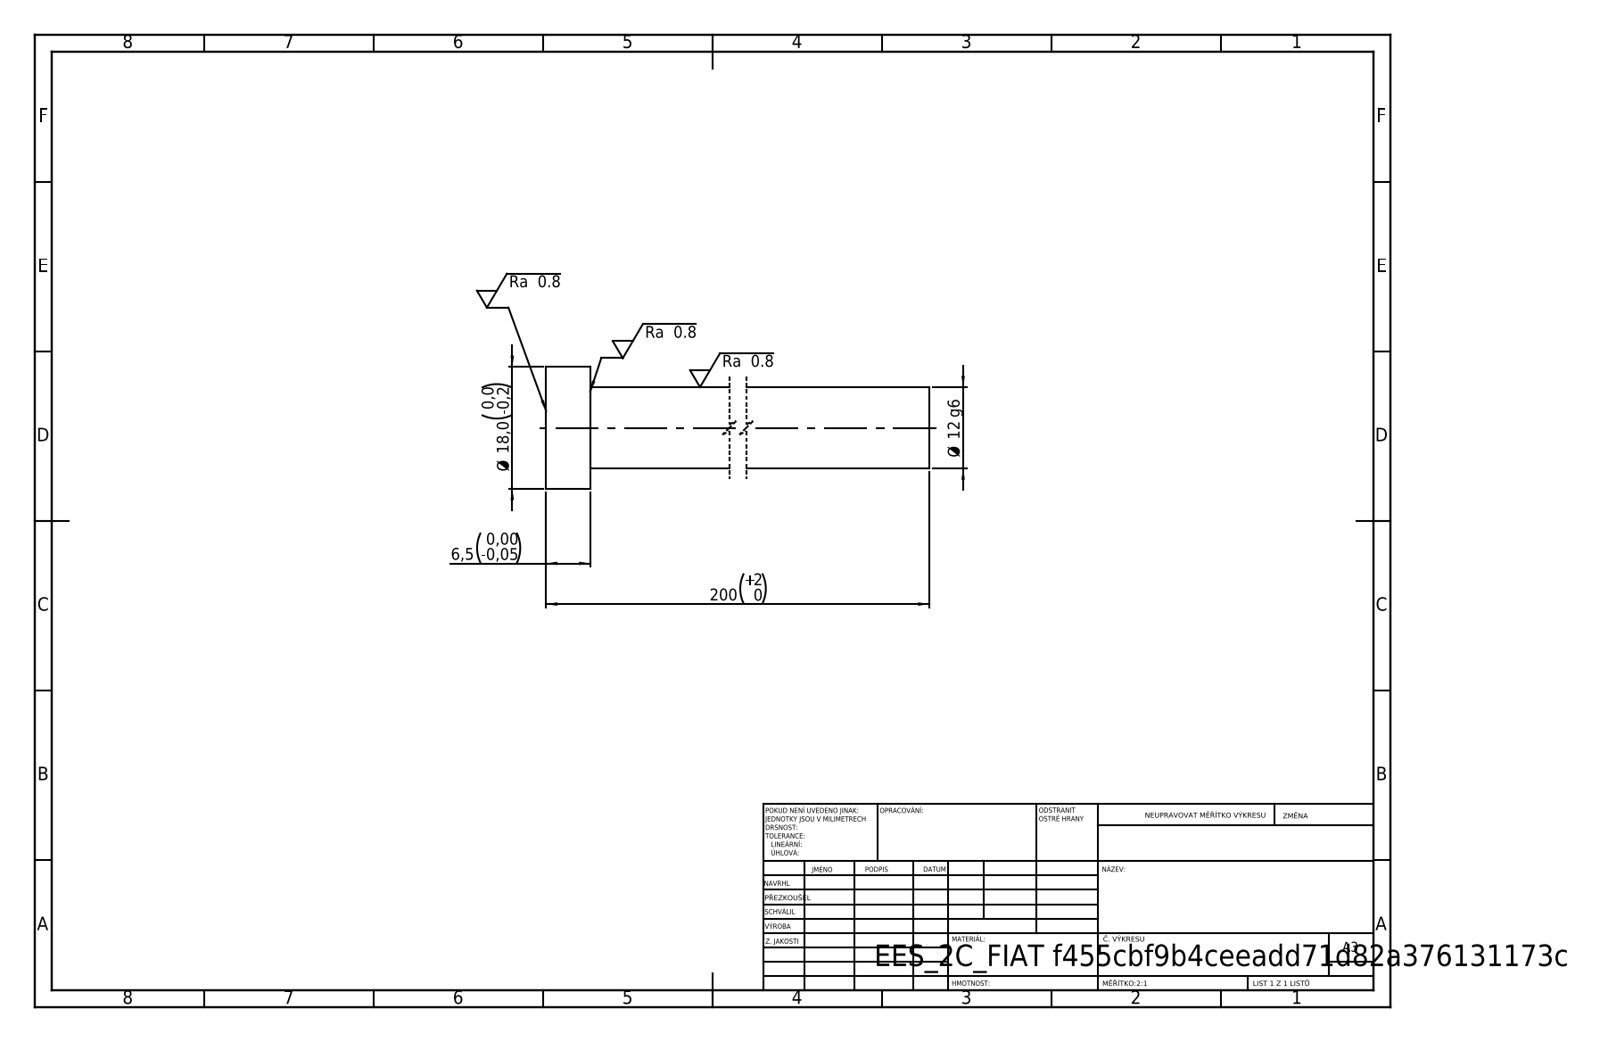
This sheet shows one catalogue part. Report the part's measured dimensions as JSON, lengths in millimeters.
{"step_written_by": "SolidWorks 2019 (CONFIG_CONTROL_DESIGN)", "units": "millimeters", "bodies": {"solids": 1, "faces": 7, "planar": 3, "cylindrical": 4, "other": 0}, "overall_size": [200, 18, 18], "volume_mm3": 23538, "surface_area_mm2": 8171, "round_bosses_or_shafts": [[18, 1], [12, 1]], "face_to_face_distances": [6.5, 200, 193.5]}
